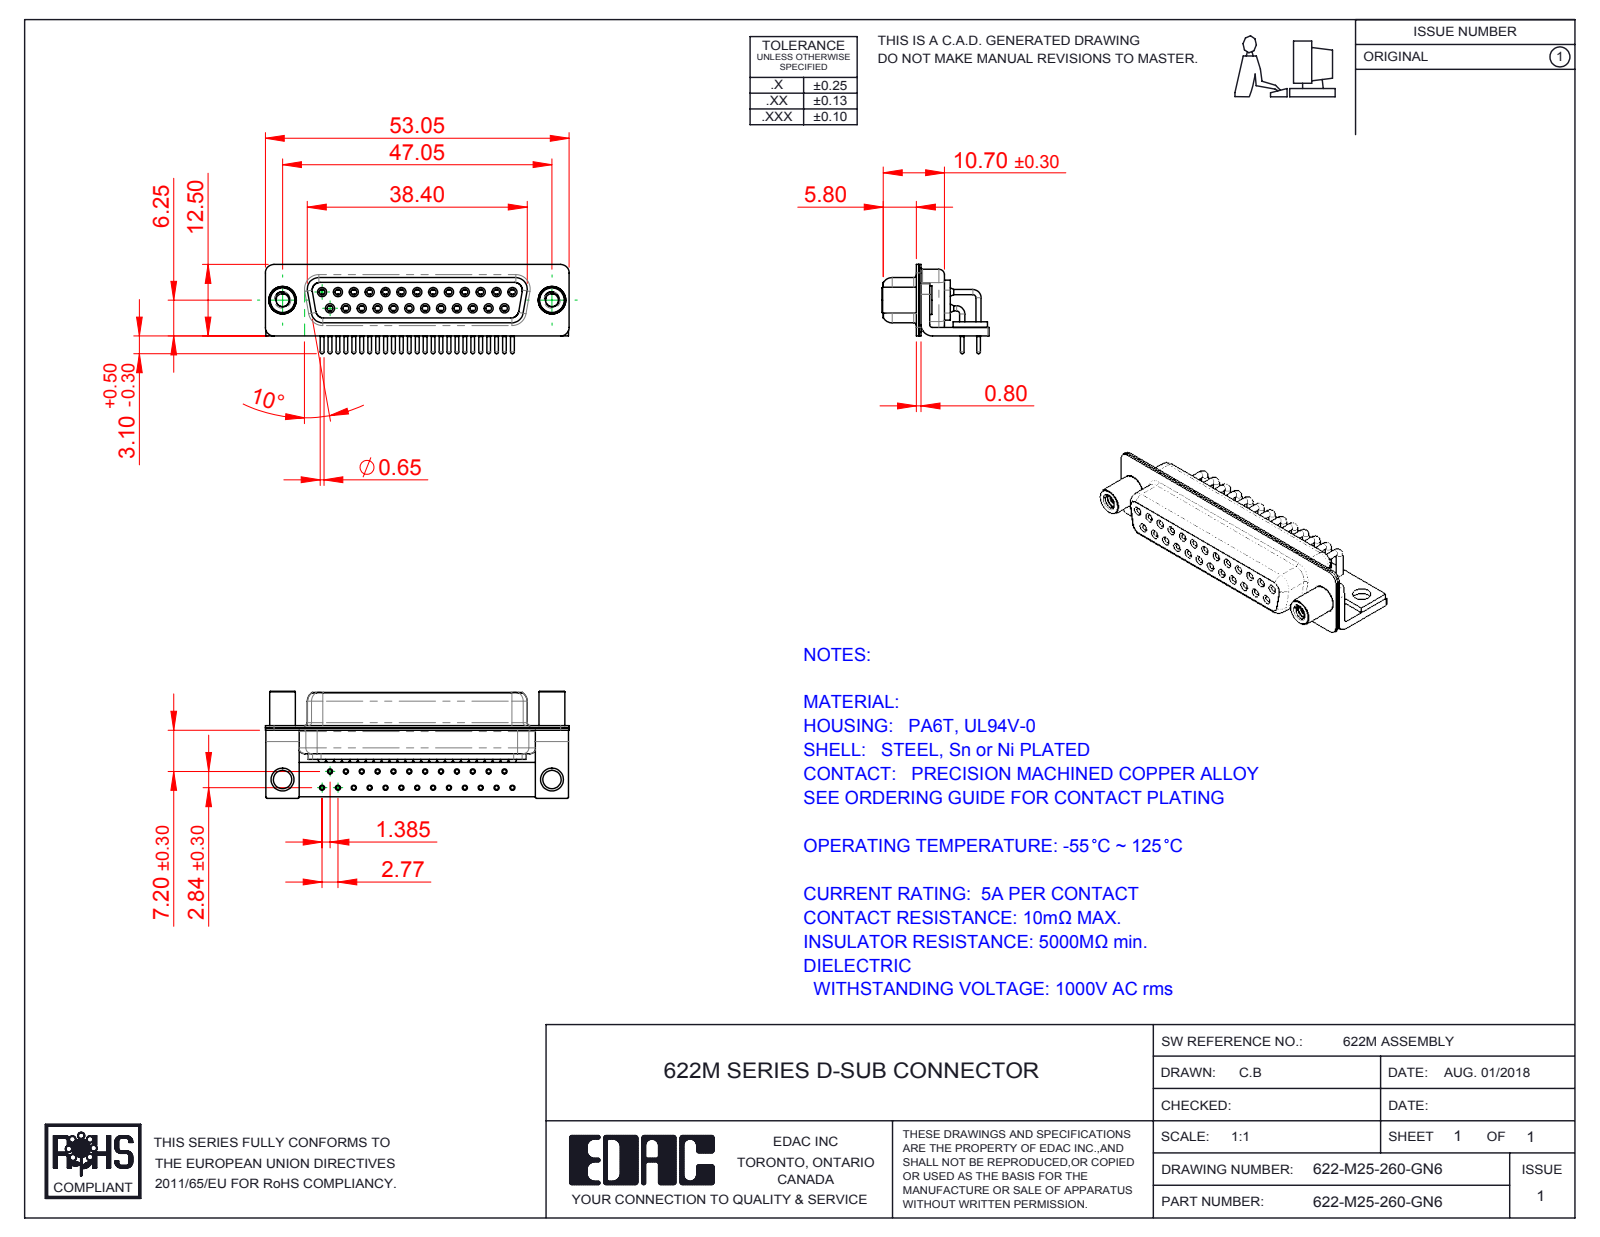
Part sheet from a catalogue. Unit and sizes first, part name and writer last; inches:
Units: inches
Overall size (bounding box): 2.089 × 0.736 × 0.614
Round holes (diameter × count): ⌀0.035 ×25, ⌀0.039 ×25, ⌀0.043 ×25, ⌀0.067 ×25, ⌀0.071 ×25, ⌀0.079 ×25, ⌀0.089 ×2, ⌀0.126 ×2, ⌀0.157 ×2, ⌀0.189 ×2
Round bosses / shafts (diameter × count): ⌀0.035 ×27, ⌀0.063 ×25, ⌀0.059 ×25, ⌀0.026 ×25, ⌀0.197 ×2, ⌀0.193 ×2, ⌀0.177 ×2
Partial cylindrical surfaces — rounded edges, fillets, slot ends (radius × count): R0.01 ×16, R0.059 ×16, R0.079 ×13, R0.053 ×8, R0.063 ×8, R0.02 ×5, R0.024 ×4, R0.026 ×4
Main face-to-face distances: 0.016, 0.091, 0.075, 0.057, 0.352, 0.033, 0.031, 0.244, 0.039, 0.335
Hole centre spacings: 0.124, 0.109, 0.218, 0.327, 0.436, 0.545, 0.654, 0.198
Volume: 0.274 in³ · Surface area: 17.24 in²
Bodies: 33 solids, 1754 faces (470 planar, 826 cylindrical, 458 other)
Part name (STEP PRODUCT): 622M 4-40 Threaded Standoff; 622M Stabilizer Bracket; 622M Contact Row 2; 622M Contact Row 1 (+5 more)
STEP written by: SolidWorks 2016 (CONFIG_CONTROL_DESIGN)
